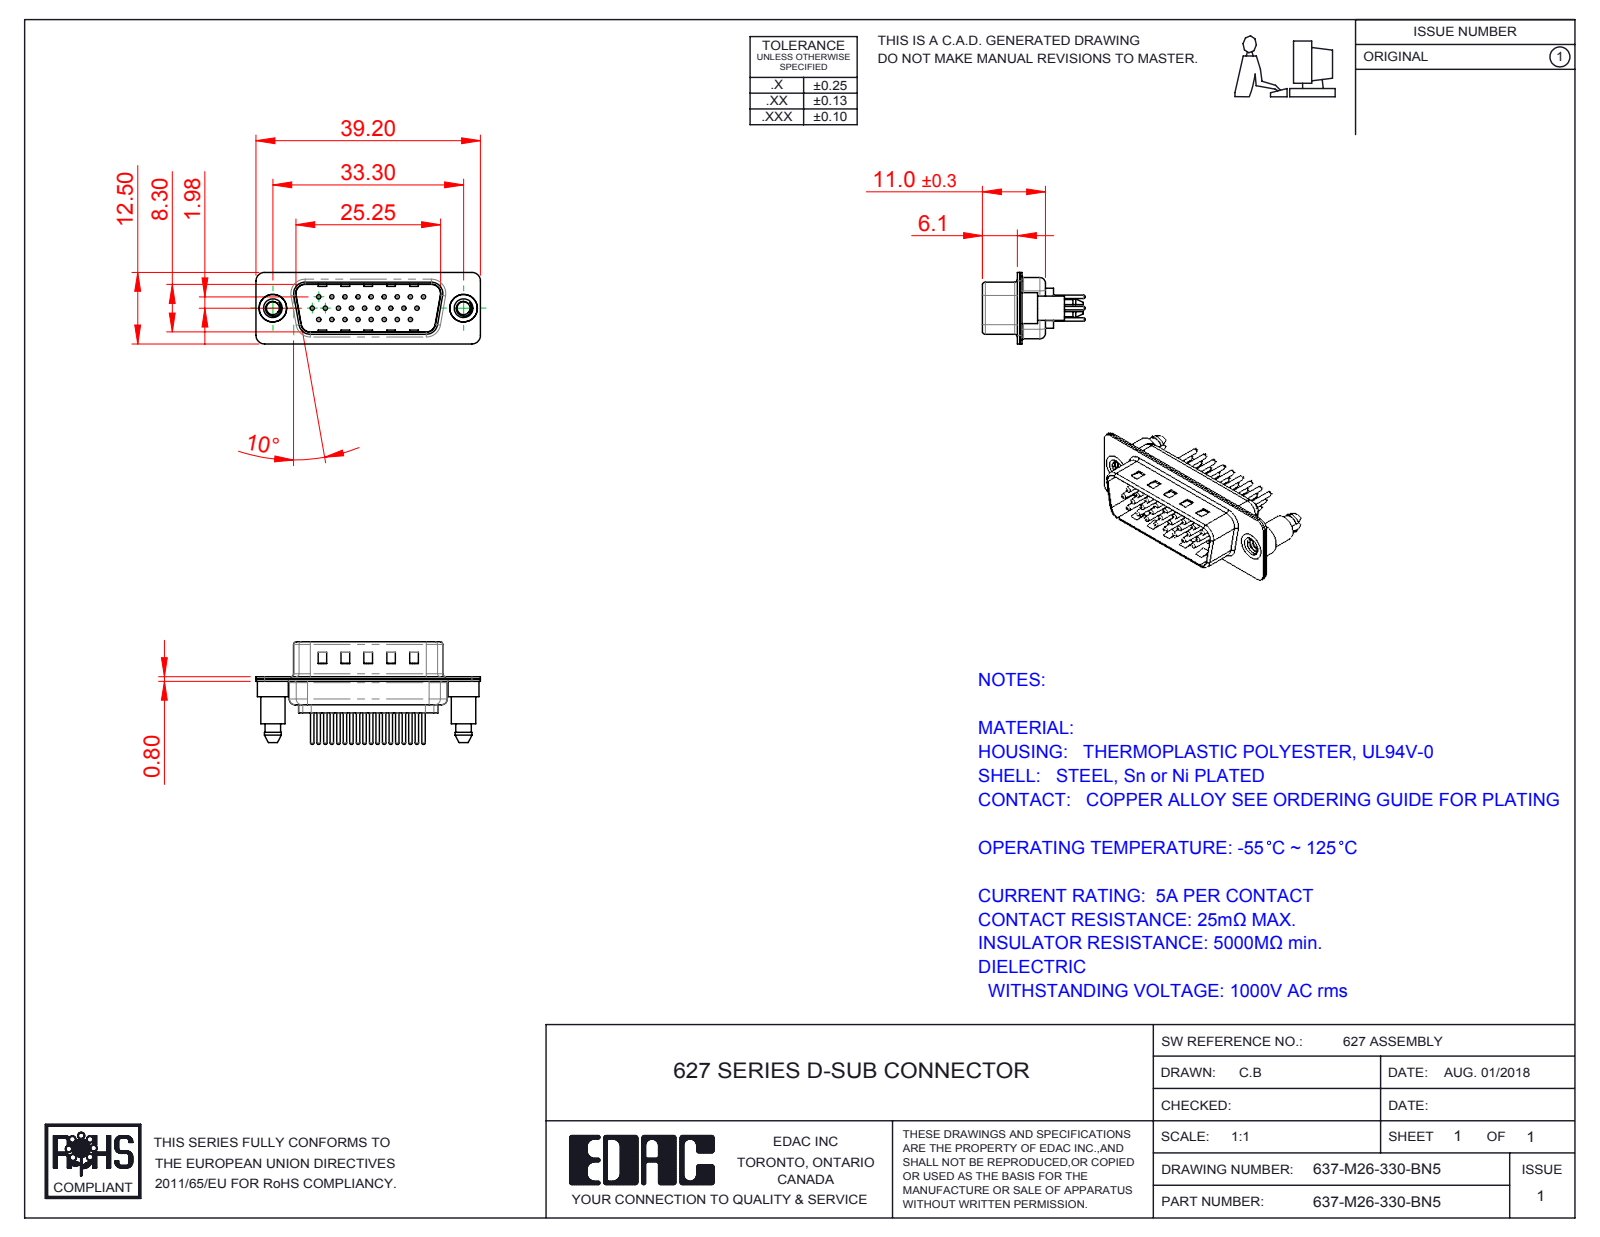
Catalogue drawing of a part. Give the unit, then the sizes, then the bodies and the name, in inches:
Units: inches
Overall size (bounding box): 1.543 × 0.705 × 0.492
Round holes (diameter × count): ⌀0.03 ×26, ⌀0.063 ×26, ⌀0.079 ×26, ⌀0.089 ×2, ⌀0.157 ×2, ⌀0.189 ×2
Round bosses / shafts (diameter × count): ⌀0.059 ×26, ⌀0.024 ×26, ⌀0.213 ×2, ⌀0.193 ×2, ⌀0.167 ×2
Partial cylindrical surfaces — rounded edges, fillets, slot ends (radius × count): R0.059 ×18, R0.079 ×12, R0.063 ×10, R0.02 ×8, R0.01 ×4, R0.024 ×4, R0.026 ×4, R0.035 ×4
Main face-to-face distances: 0.016, 0.031, 0.374, 0.358, 0.343, 0.39, 0.248, 0.03, 0.217, 0.014
Hole centre spacings: 0.156, 0.09, 0.18, 0.238, 0.09, 0.324, 0.27, 0.413
Volume: 0.125 in³ · Surface area: 9.43 in²
Bodies: 31 solids, 1352 faces (337 planar, 529 cylindrical, 486 other)
Part name (STEP PRODUCT): 637M Housing_26 Contacts; 637M Shell Front_26 Contacts; 637M Shell Rear_26 Contacts; 637M Contact Row 1_30 (+4 more)
STEP written by: SolidWorks 2016 (CONFIG_CONTROL_DESIGN)
